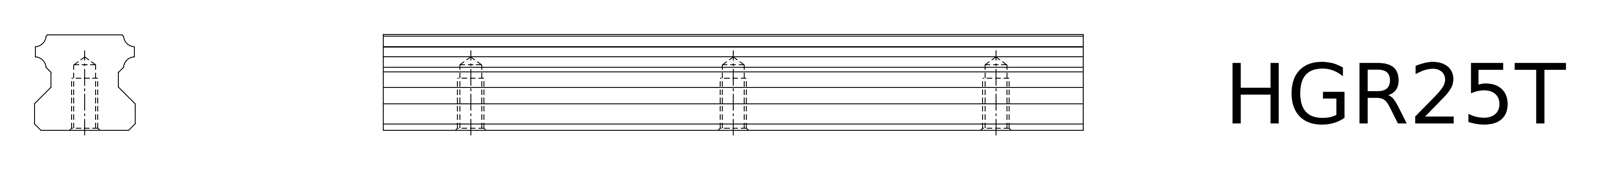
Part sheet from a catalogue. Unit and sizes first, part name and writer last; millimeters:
Units: millimetres
Overall size (bounding box): 150 × 23 × 22
Round holes (diameter × count): ⌀6 ×3
Partial cylindrical surfaces — rounded edges, fillets, slot ends (radius × count): R0.5 ×12, R1 ×6, R2.43 ×4
Main face-to-face distances: 22, 23, 3.6, 19.4, 19.61, 150, 15.8, 11.01, 8.6, 28.56
Hole centre spacings: 60, 120
Volume: 64 745 mm³ · Surface area: 15 200 mm²
Bodies: 1 solid, 53 faces (25 planar, 28 cylindrical, 0 other)
Part name (STEP PRODUCT): HGR25T
STEP written by: SolidWorks 2006104 (CONFIG_CONTROL_DESIGN)
